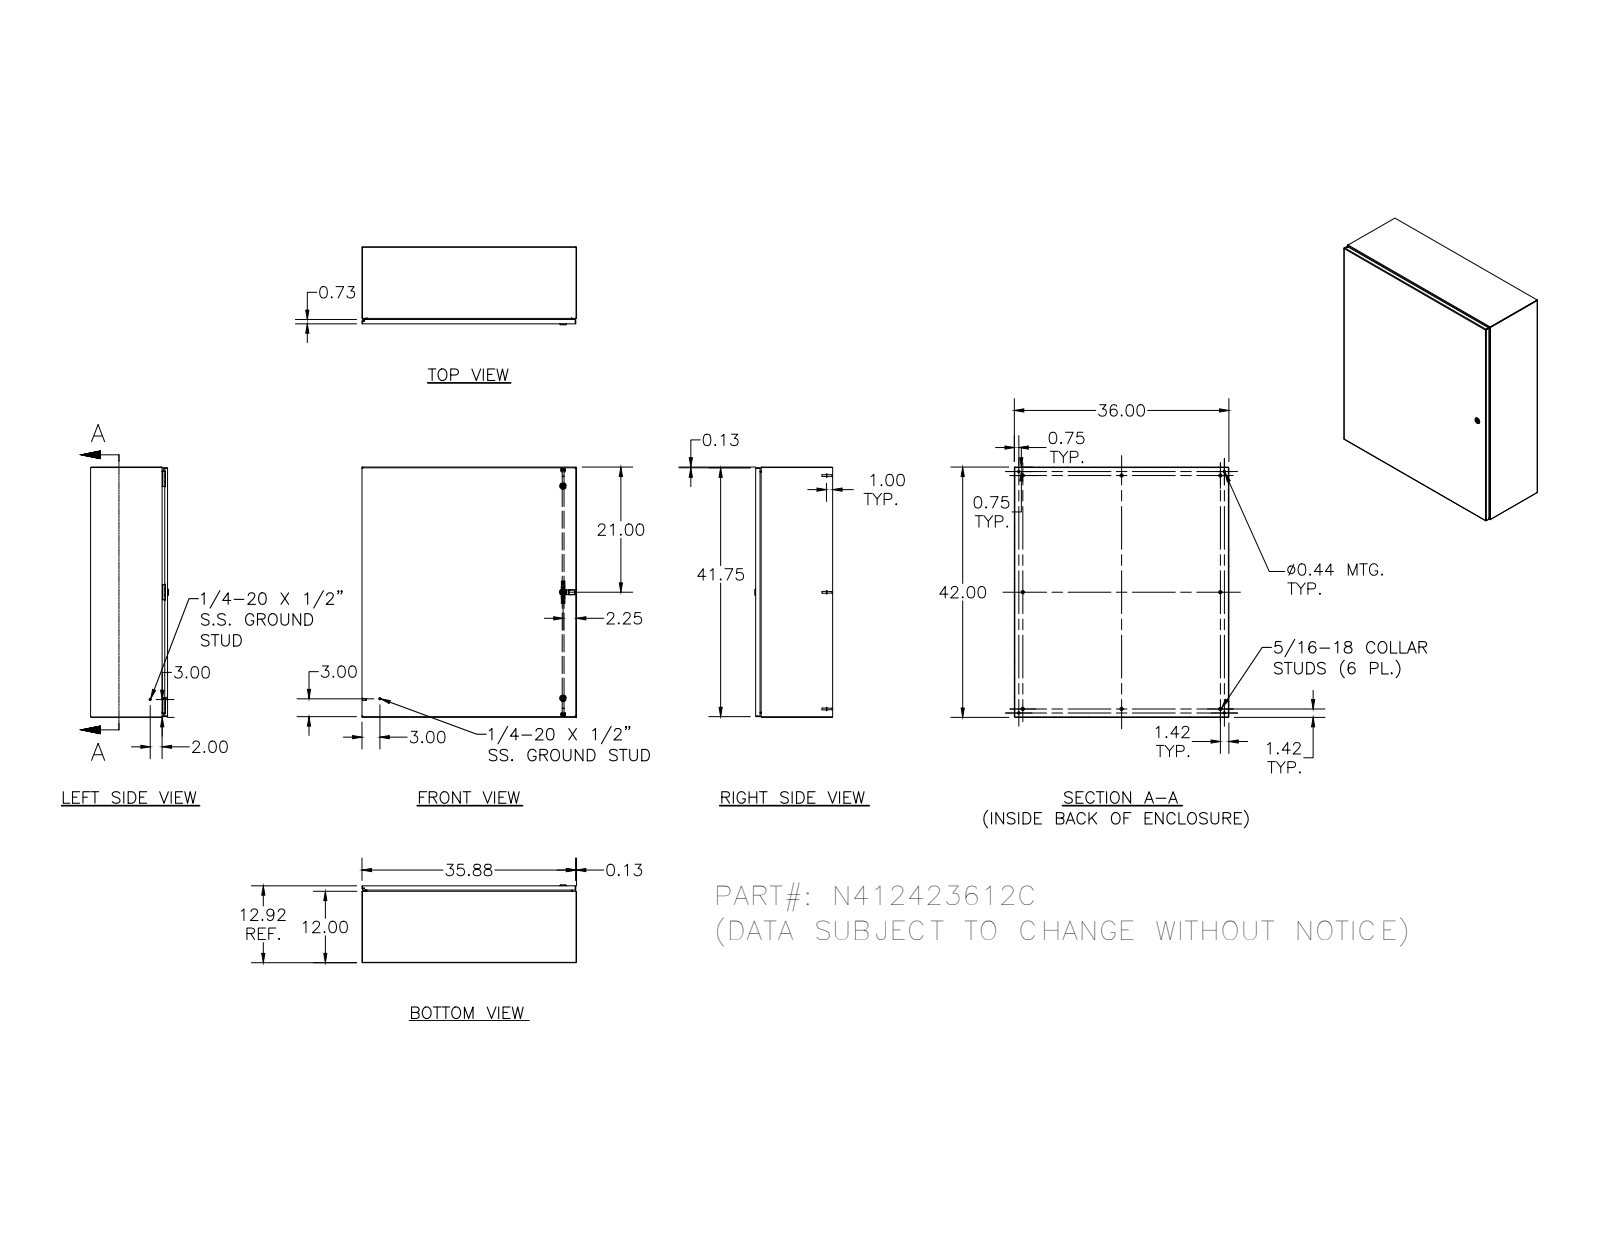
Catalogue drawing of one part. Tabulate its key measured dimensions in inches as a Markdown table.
| quantity | value |
| --- | --- |
| part name | N412423612C; N412423612CBLR; N4123612CTB; N4124236CLID (+8 more) |
| STEP written by | Autodesk Inventor 2011 (AUTOMOTIVE_DESIGN) |
| units | inches |
| bodies | 72 solids, 2241 faces (871 planar, 820 cylindrical, 550 other) |
| overall size | 42 × 36 × 13.075 |
| volume | 389.9 in³ |
| surface area | 10 519 in² |
| round holes (diameter × count) | 0.188 × 7, 0.093 × 6, 0.152 × 6, 0.167 × 6, 0.172 × 6, 0.197 × 5, 0.165 × 4, 0.438 × 4, 0.156 × 3, 0.106 × 2, 0.16 × 2, 0.169 × 2 |
| round bosses / shafts (diameter × count) | 0.25 × 14, 0.563 × 8, 0.3 × 8, 0.275 × 8, 0.36 × 6, 0.32 × 6, 0.256 × 6, 0.164 × 6 |
| partial cylindrical surfaces (radius × count) | 0.05 × 38, 0.031 × 32, 0.012 × 30, 0.016 × 26, 0.125 × 24, 0.02 × 20, 0.105 × 18, 0.118 × 16 |
| main face-to-face distances | 0.074, 12.843, 12.769, 12.917, 35.926, 41.926, 35.852, 36, 41.852, 42 |
| hole center spacings | 19, 19.004, 33.361, 38.004, 0.5, 0.656, 0.66, 18.344 |
